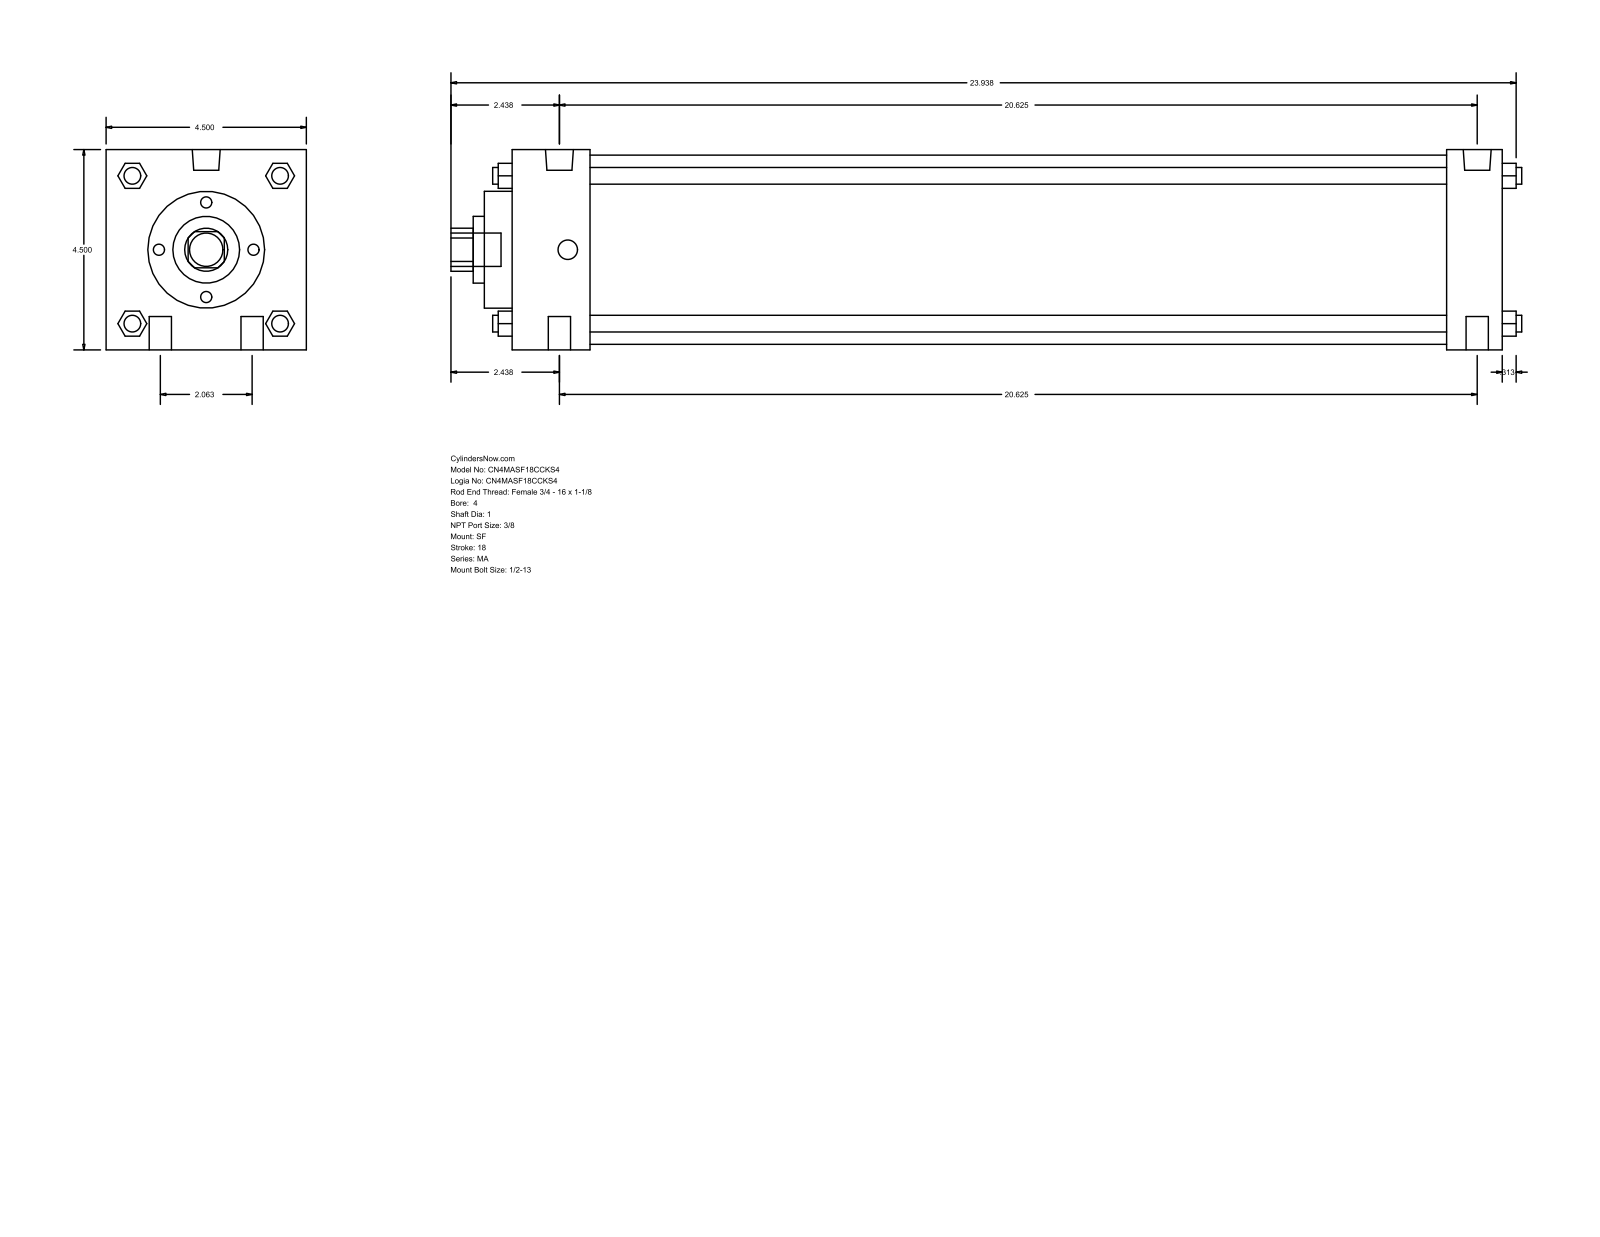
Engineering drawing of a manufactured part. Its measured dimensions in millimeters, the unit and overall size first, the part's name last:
Units: millimetres
Overall size (bounding box): 611.19 × 114.3 × 114.3
Round holes (diameter × count): ⌀25.4 ×1, ⌀38.1 ×1, ⌀66.67 ×1, ⌀107.95 ×1
Round bosses / shafts (diameter × count): ⌀12.7 ×4, ⌀9.53 ×4, ⌀15.93 ×2, ⌀11.11 ×2, ⌀19.05 ×1
Partial cylindrical surfaces — rounded edges, fillets, slot ends (radius × count): R12.29 ×1
Main face-to-face distances: 114.3, 565.16, 533.41, 31.75, 44.46, 488.95, 520.7, 15.87, 60.33, 549.28
Bodies: 0 solids, 126 faces (95 planar, 31 cylindrical, 0 other)
Part name (STEP PRODUCT): MA_SF__0400_1
STEP written by: GSSL Pune (CONFIG_CONTROL_DESIGN)
